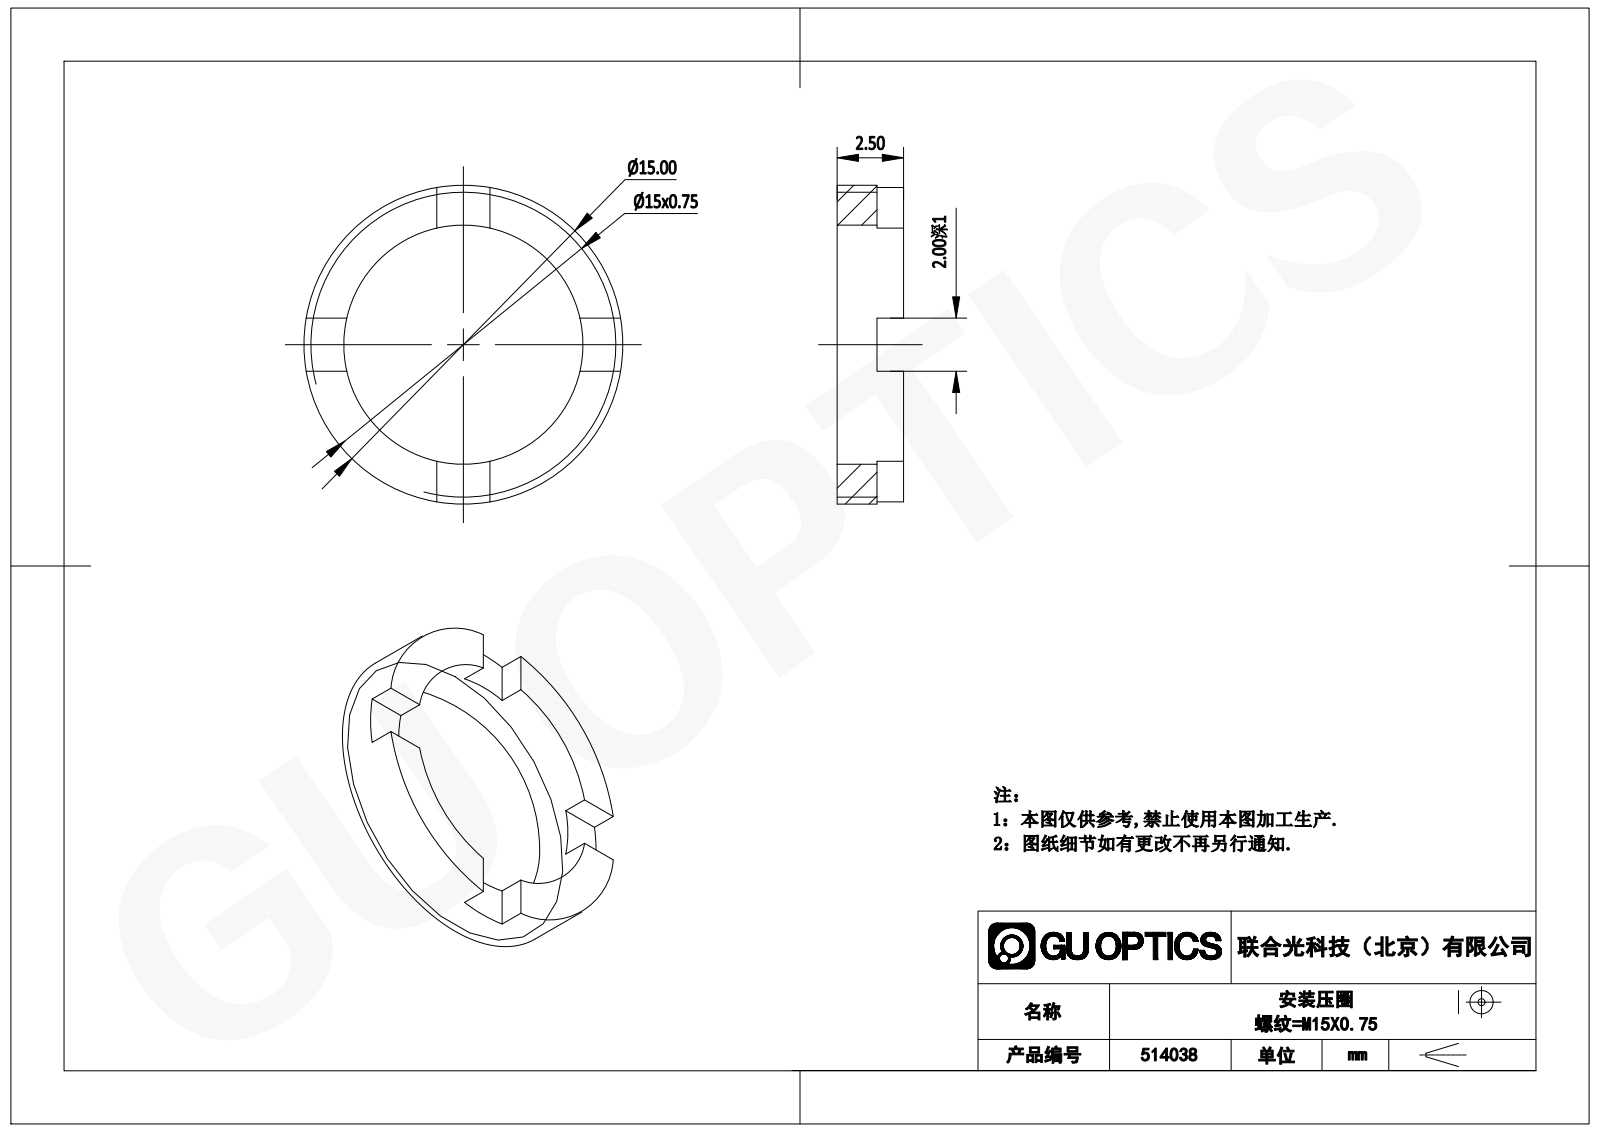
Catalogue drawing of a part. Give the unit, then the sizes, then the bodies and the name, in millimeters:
Units: millimetres
Overall size (bounding box): 15 × 15 × 2.5
Round holes (diameter × count): ⌀12 ×1
Round bosses / shafts (diameter × count): ⌀15 ×1
Main face-to-face distances: 2.5, 1.5, 1, 2
Volume: 147 mm³ · Surface area: 335 mm²
Bodies: 1 solid, 21 faces (17 planar, 4 cylindrical, 0 other)
Part name (STEP PRODUCT): 514038
STEP written by: SolidWorks 2020 (CONFIG_CONTROL_DESIGN)
